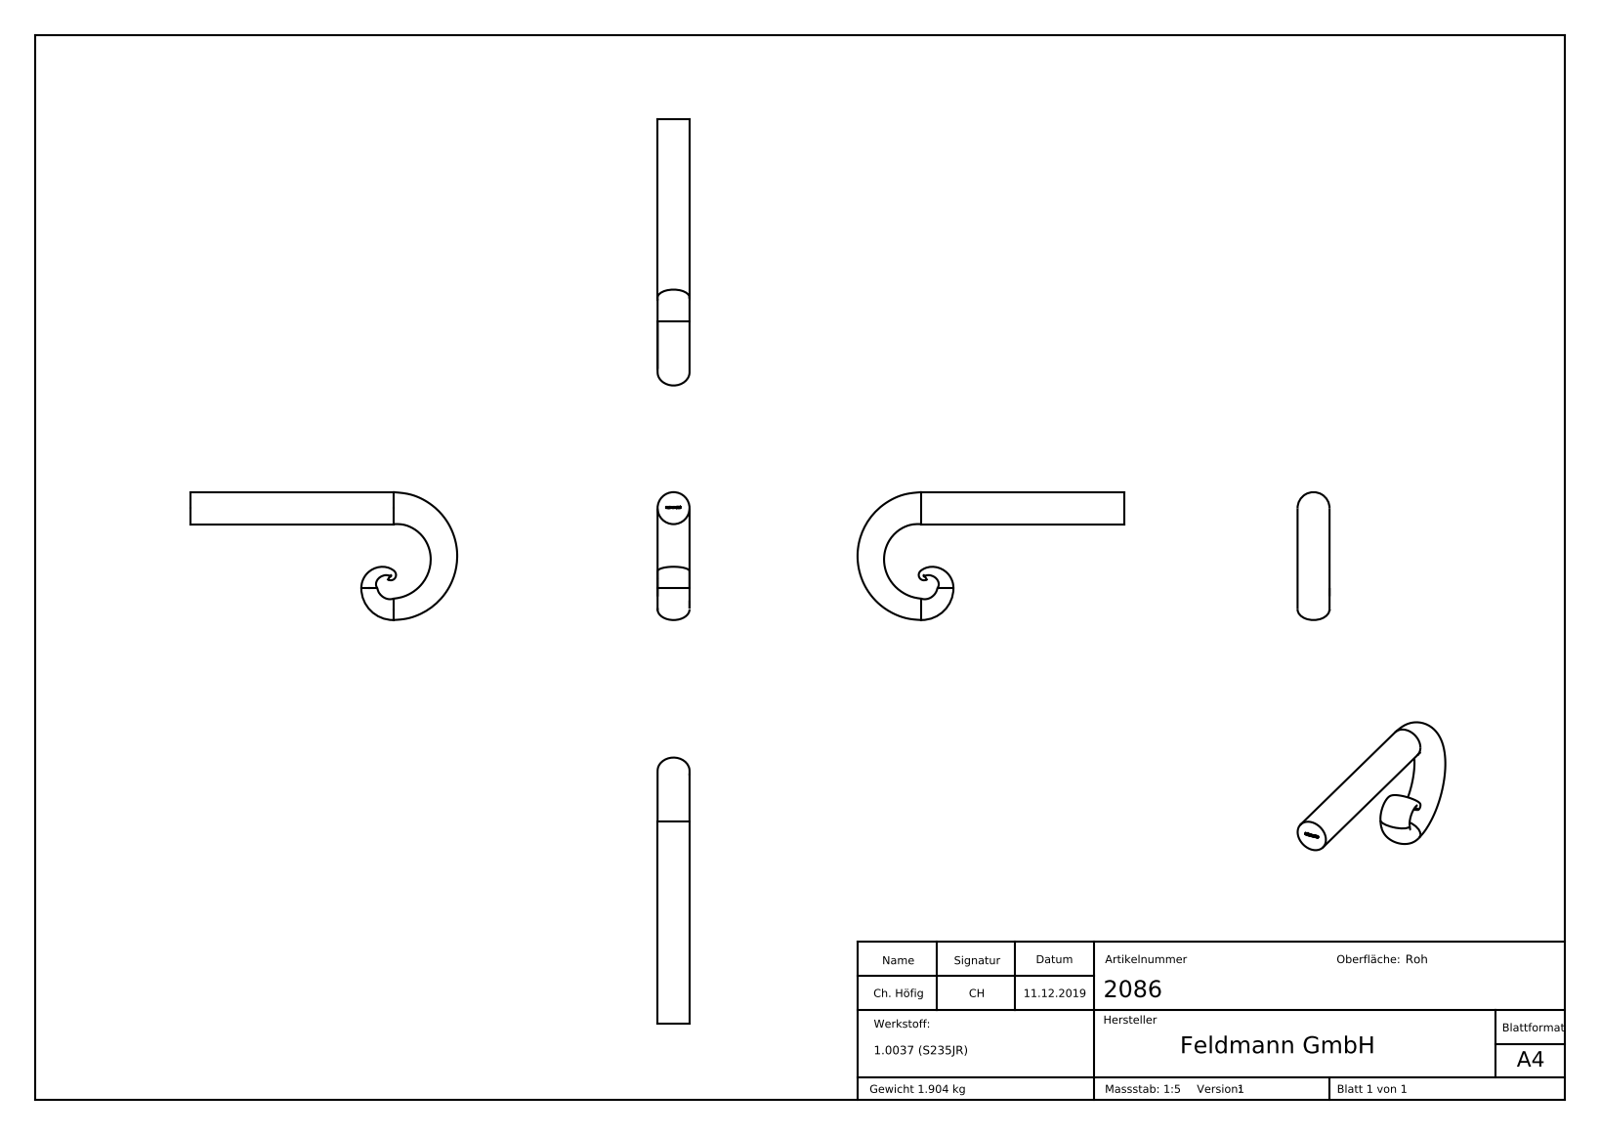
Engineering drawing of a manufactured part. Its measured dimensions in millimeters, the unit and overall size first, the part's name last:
Units: millimetres
Overall size (bounding box): 250 × 120 × 30.01
Round bosses / shafts (diameter × count): ⌀30 ×1
Main face-to-face distances: 0.39, 2.97, 1.12, 4.09, 0.73, 1.26, 3.27, 1.32, 1.65, 3.66
Volume: 244 217 mm³ · Surface area: 36 872 mm²
Bodies: 1 solid, 177 faces (84 planar, 1 cylindrical, 92 other)
Part name (STEP PRODUCT): 2086
STEP written by: SolidWorks 2015 (CONFIG_CONTROL_DESIGN)
